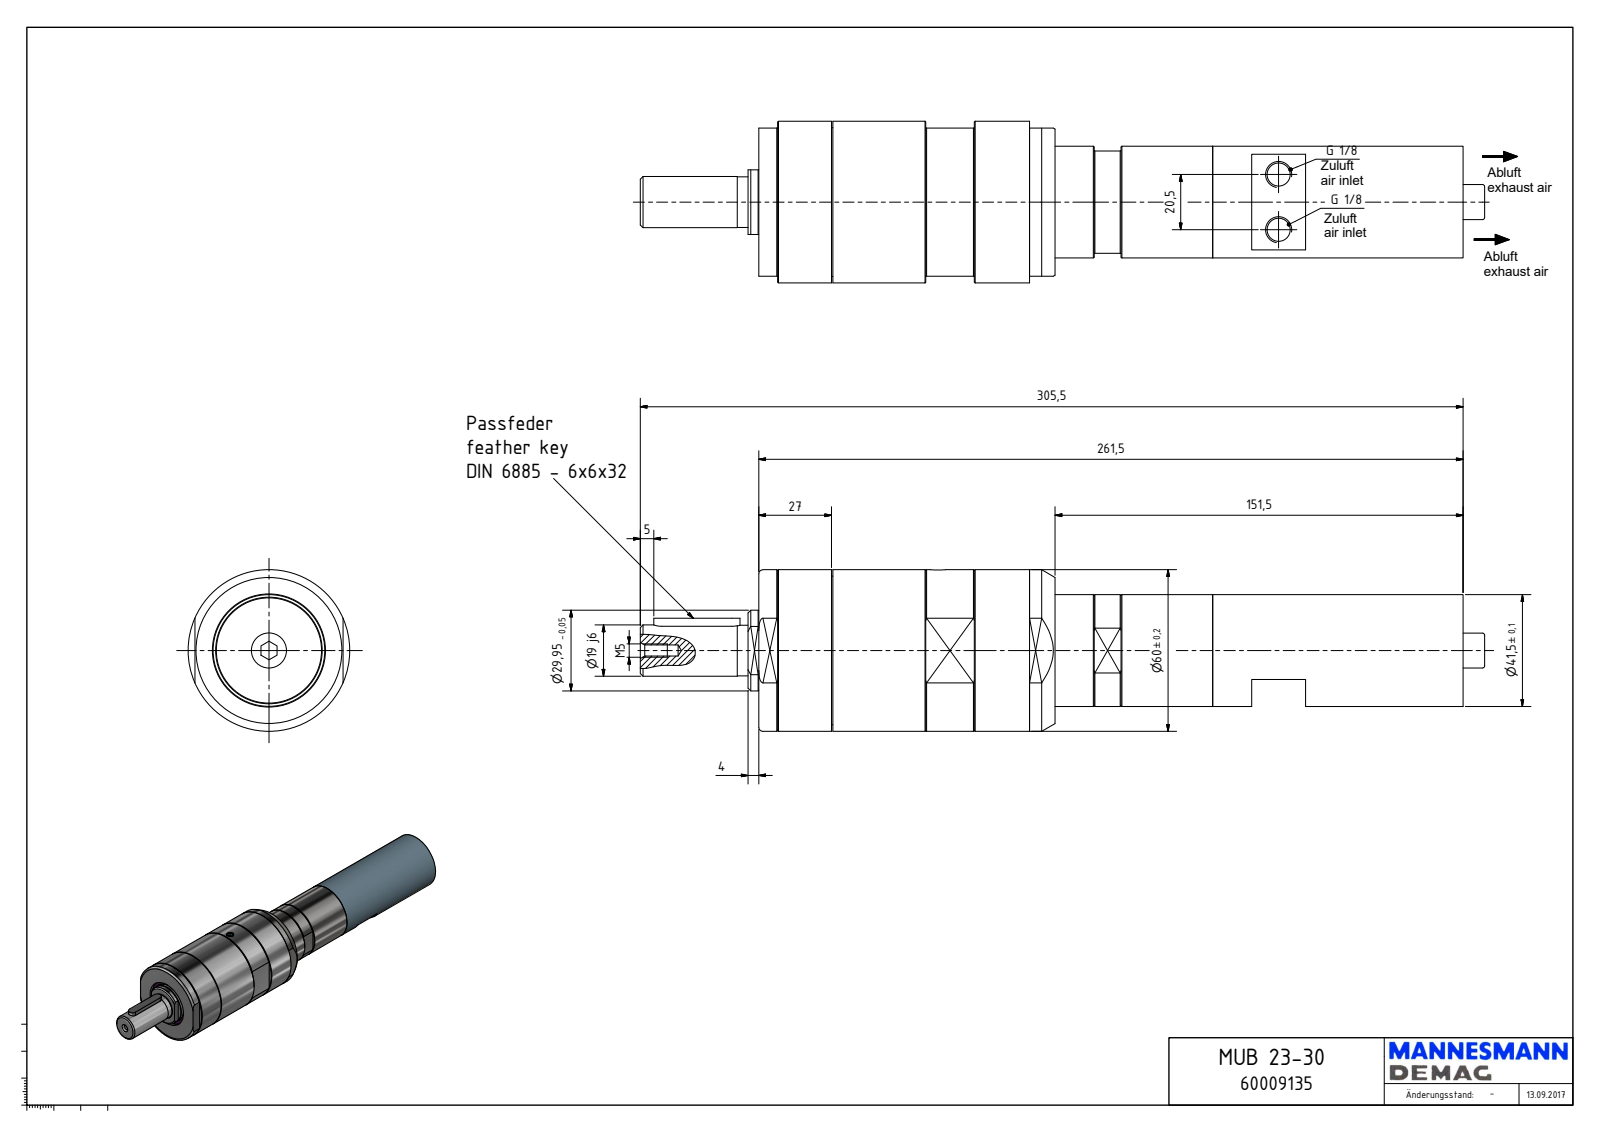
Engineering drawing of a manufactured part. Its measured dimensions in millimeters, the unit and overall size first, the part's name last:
Units: millimetres
Overall size (bounding box): 313.5 × 60 × 60
Round holes (diameter × count): ⌀8.57 ×2, ⌀1.55 ×1, ⌀4 ×1, ⌀4.13 ×1, ⌀5.5 ×1, ⌀8.5 ×1, ⌀13 ×1, ⌀35 ×1, ⌀39.5 ×1, ⌀42 ×1, ⌀55.38 ×1
Round bosses / shafts (diameter × count): ⌀60 ×1, ⌀55.18 ×1, ⌀41.5 ×1, ⌀39 ×1, ⌀36 ×1, ⌀29.95 ×1, ⌀19 ×1, ⌀18.8 ×1
Partial cylindrical surfaces — rounded edges, fillets, slot ends (radius × count): R11.68 ×94, R3.5 ×8, R1 ×2, R1.6 ×2, R2 ×2, R2.5 ×2, R3 ×2, R10.7 ×2
Main face-to-face distances: 261.5, 110, 151.5, 55, 82.5, 78.5, 27.5, 234, 104.5, 31
Hole centre spacings: 126.91, 20.5
Volume: 518 047 mm³ · Surface area: 57 456 mm²
Bodies: 1 solid, 476 faces (173 planar, 261 cylindrical, 42 other)
Part name (STEP PRODUCT): MUB 23-30_60009135
STEP written by: Autodesk Inventor 2018 (AUTOMOTIVE_DESIGN)
